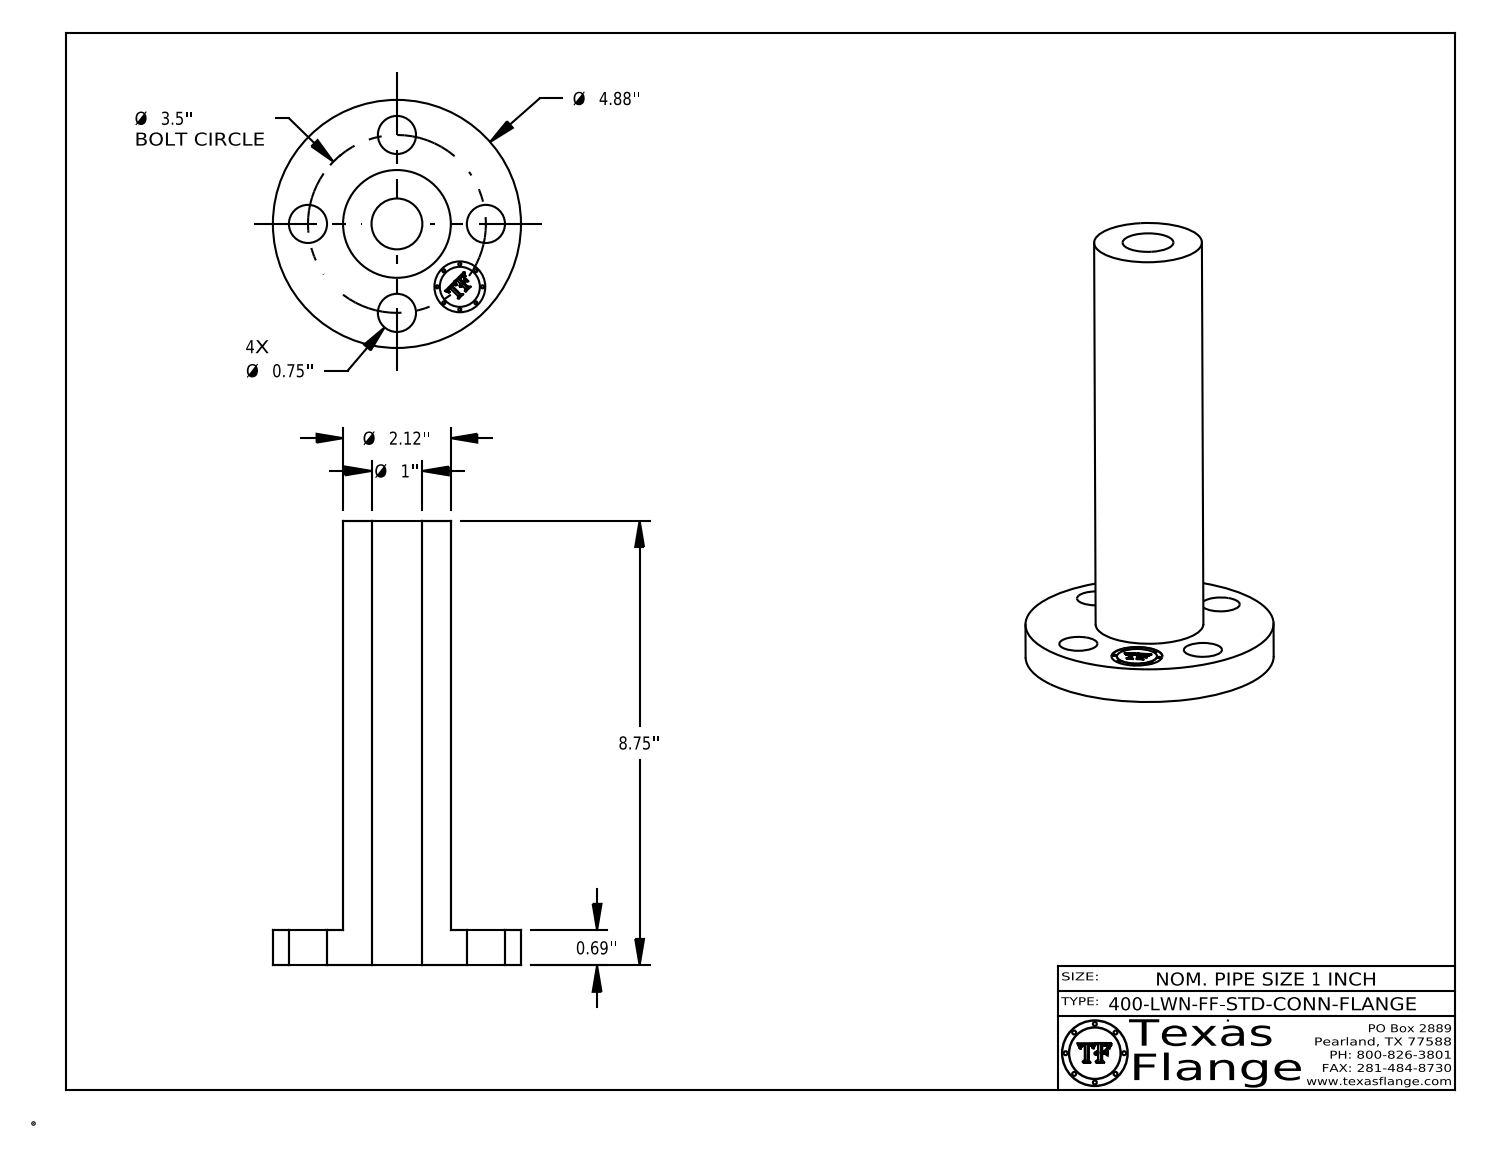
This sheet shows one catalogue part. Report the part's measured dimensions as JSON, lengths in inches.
{"part_name": "1-400-LWN-FF-STD-CONN-FLANGE", "step_written_by": "CATIA V5 STEP AP214 (AUTOMOTIVE_DESIGN)", "units": "inches", "bodies": {"solids": 1, "faces": 402, "planar": 368, "cylindrical": 34, "other": 0}, "overall_size": [8.75, 4.88, 4.88], "volume_in3": 33.26, "surface_area_in2": 130.6, "round_holes": [[0.75, 4], [1, 2]], "round_bosses_or_shafts": [[0.061, 8], [4.88, 1], [2.12, 1], [0.788, 1]], "face_to_face_distances": [0.69, 8.75, 8.06, 0.685, 8.065, 0.298, 0.293, 0.054, 0.193, 0.248], "hole_center_spacings": [1.75, 2.475, 1.339, 3.233, 3.5]}
